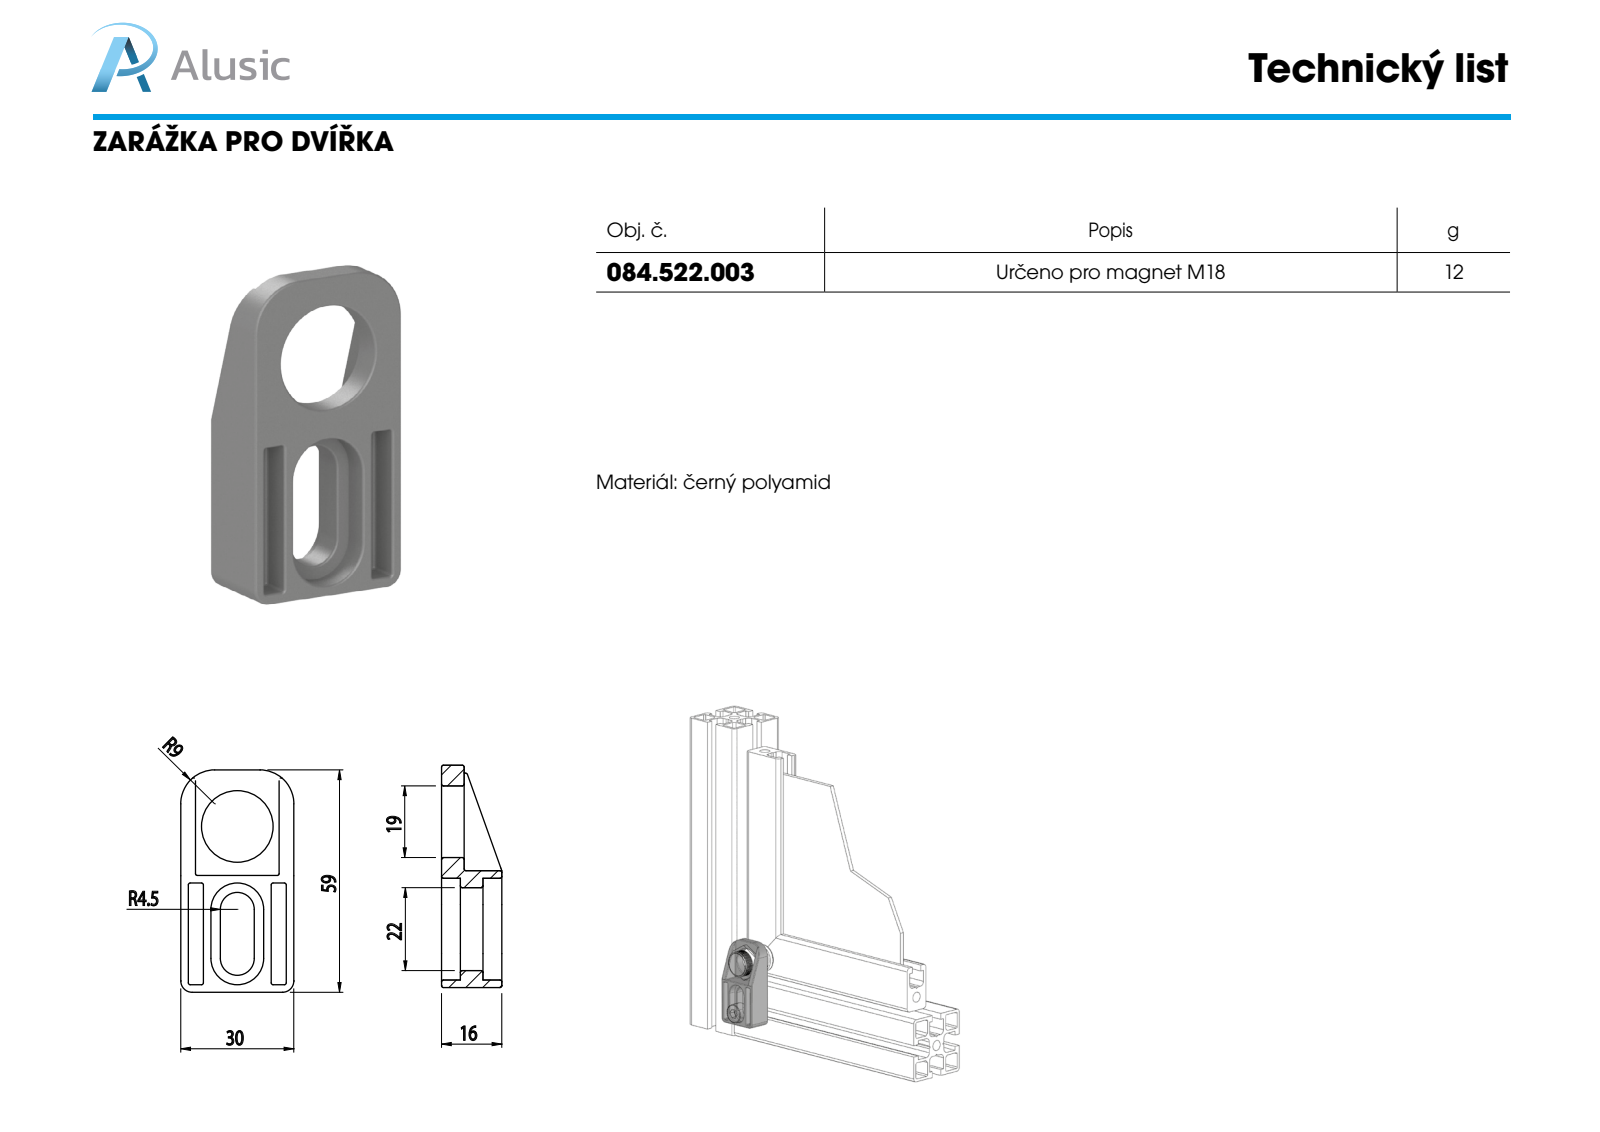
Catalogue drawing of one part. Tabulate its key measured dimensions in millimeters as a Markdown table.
| quantity | value |
| --- | --- |
| part name | 084.522.003 |
| STEP written by | SolidWorks 2016 (CONFIG_CONTROL_DESIGN) |
| units | millimeters |
| bodies | 1 solid, 213 faces (40 planar, 95 cylindrical, 78 other) |
| overall size | 59 × 30 × 16 |
| volume | 11 949 mm³ |
| surface area | 7 788 mm² |
| round holes (diameter × count) | 19 × 1 |
| partial cylindrical surfaces (radius × count) | 0.5 × 61, 3 × 2, 4.5 × 2, 7 × 2, 9 × 2 |
| main face-to-face distances | 6, 2, 22, 30, 4, 28, 24, 5, 16, 10 |
